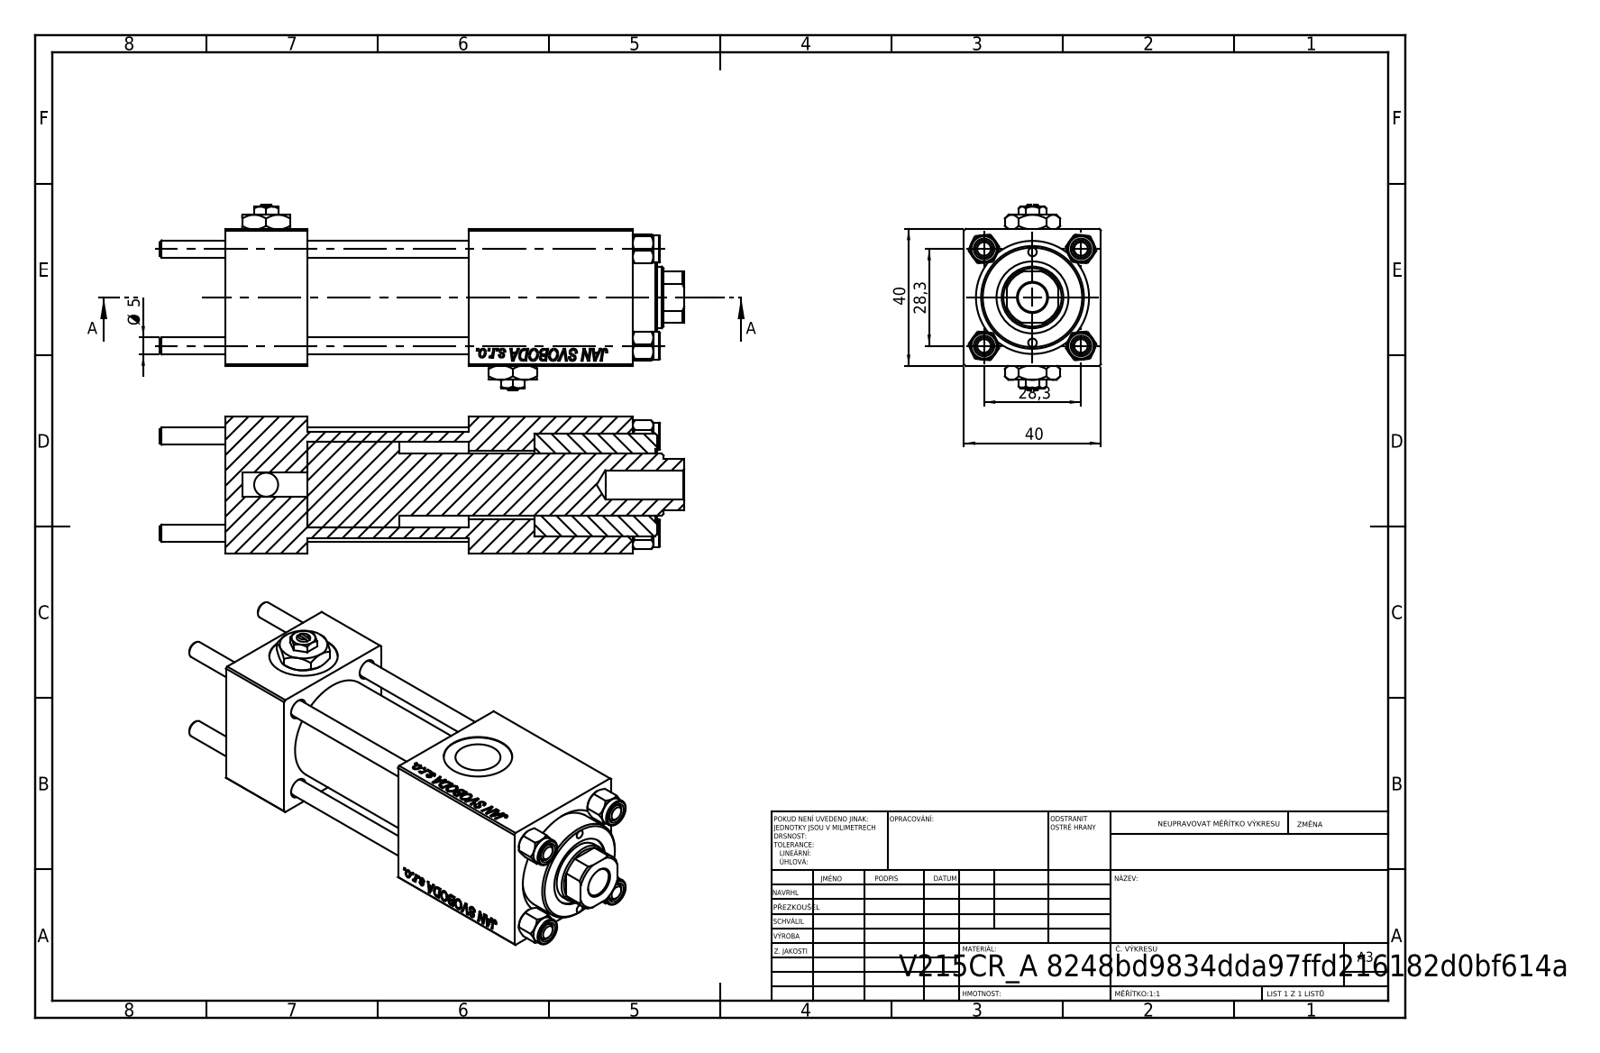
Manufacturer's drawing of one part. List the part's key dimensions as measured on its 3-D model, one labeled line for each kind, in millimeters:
Part name (STEP PRODUCT): V215CR_BODY_A; CR025_012_A_0_G_A_G_M_020_+#_##_TYCINKA; V215CR_VCP; V215_VC_A (+2 more)
STEP written by: SolidWorks 2019 (CONFIG_CONTROL_DESIGN)
Units: millimetres
Bodies: 13 solids, 1235 faces (565 planar, 92 cylindrical, 578 other)
Overall size (bounding box): 153 × 54 × 40
Volume: 150 909 mm³ · Surface area: 63 103 mm²
Round holes (diameter × count): ⌀5 ×4, ⌀20 ×3, ⌀2.5 ×2, ⌀7 ×2, ⌀13.16 ×2, ⌀8.5 ×1, ⌀18 ×1, ⌀21 ×1, ⌀25 ×1, ⌀30 ×1
Round bosses / shafts (diameter × count): ⌀8 ×4, ⌀31 ×1
Partial cylindrical surfaces — rounded edges, fillets, slot ends (radius × count): R8.5 ×1
Main face-to-face distances: 40, 24, 39.8, 47, 71, 90.3, 66.3, 19.3, 95, 119
Hole centre spacings: 14.18, 20.01, 28.3, 30.84, 13.25, 40.02, 26.5, 72
